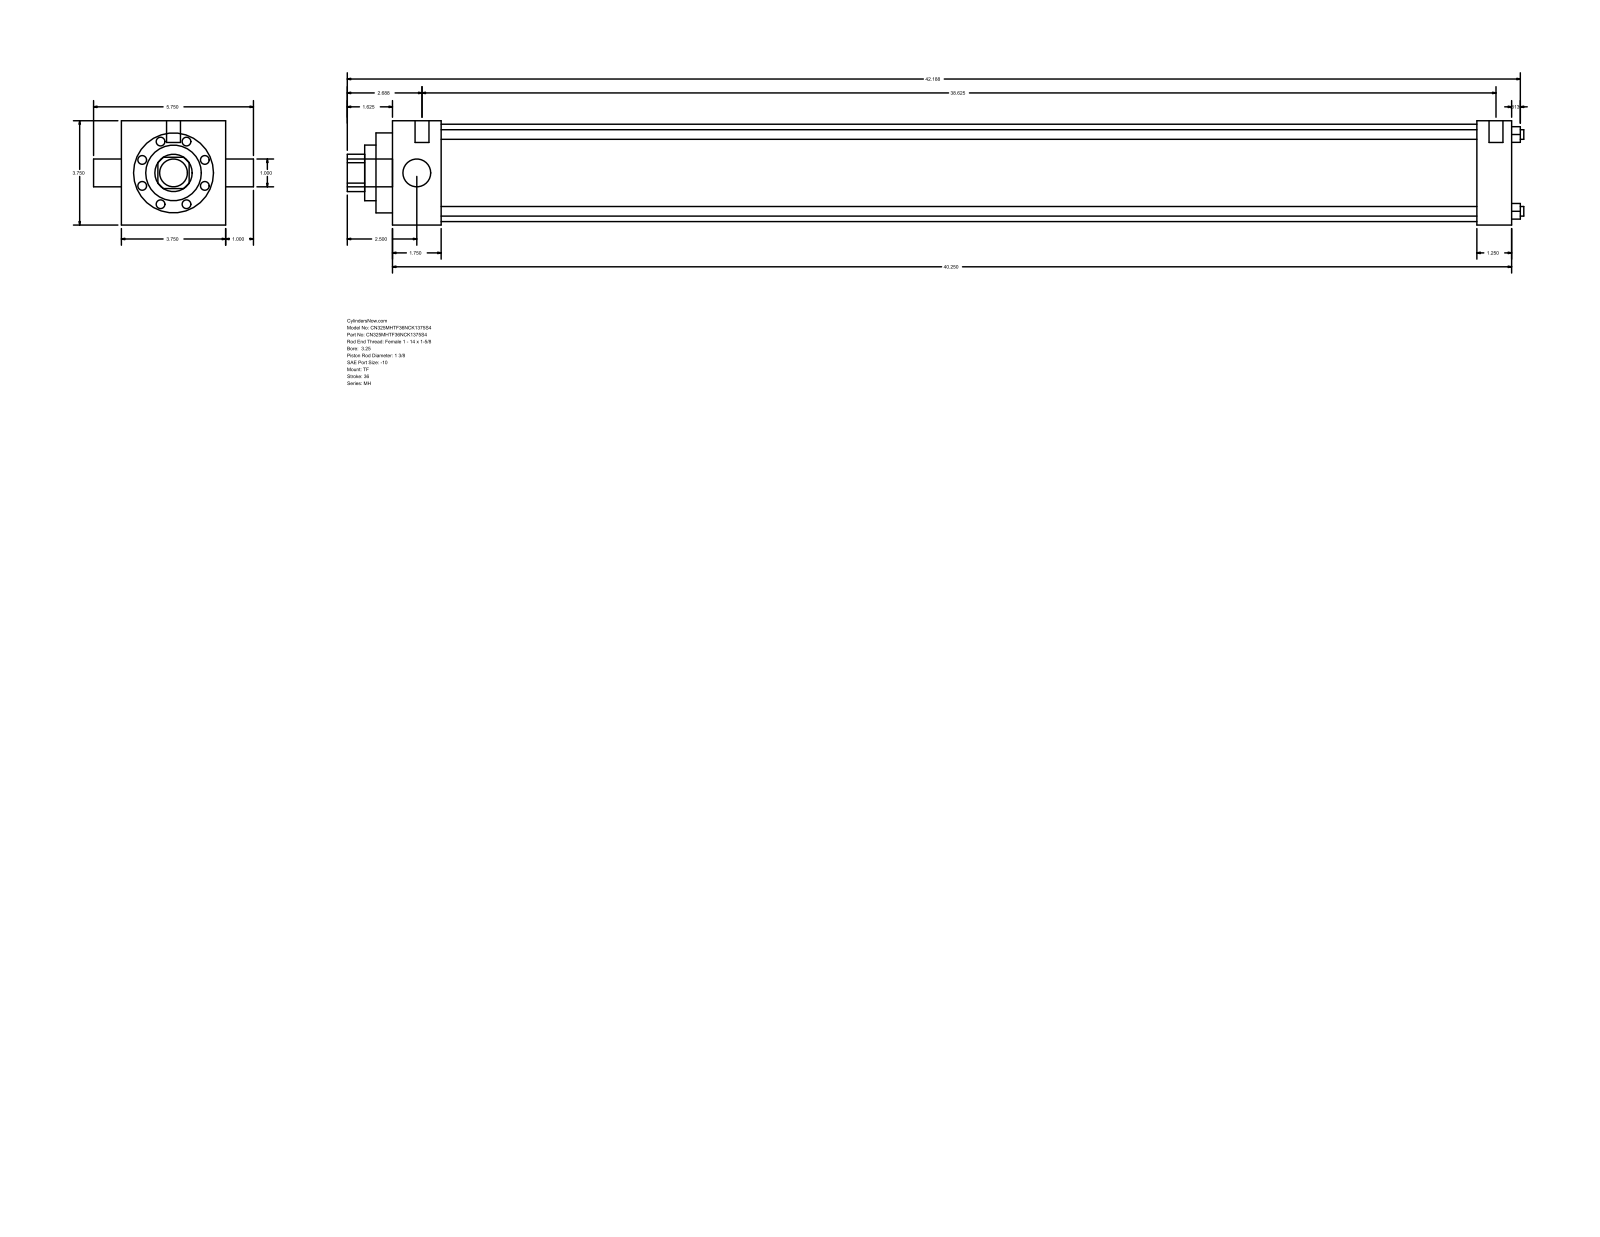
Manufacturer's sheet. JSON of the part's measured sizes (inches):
{"part_name": "MH_TF__0325_1.375", "step_written_by": "GSSL Pune (CONFIG_CONTROL_DESIGN)", "units": "inches", "bodies": {"solids": 0, "faces": 86, "planar": 61, "cylindrical": 25, "other": 0}, "overall_size": [42.313, 5.75, 3.75], "round_holes": [[0.345, 4], [1, 1], [1.375, 1], [2, 1], [2.875, 1], [3.5, 1]], "round_bosses_or_shafts": [[0.219, 3], [0.5, 2], [1, 1]], "partial_cylinders_radius": [[0.672, 1]], "face_to_face_distances": [3.75, 40.25, 1.75, 39, 37.25, 38.5, 1.25, 0.594, 2.344, 39.594], "hole_center_spacings": [1.952, 2.76, 3.903]}
